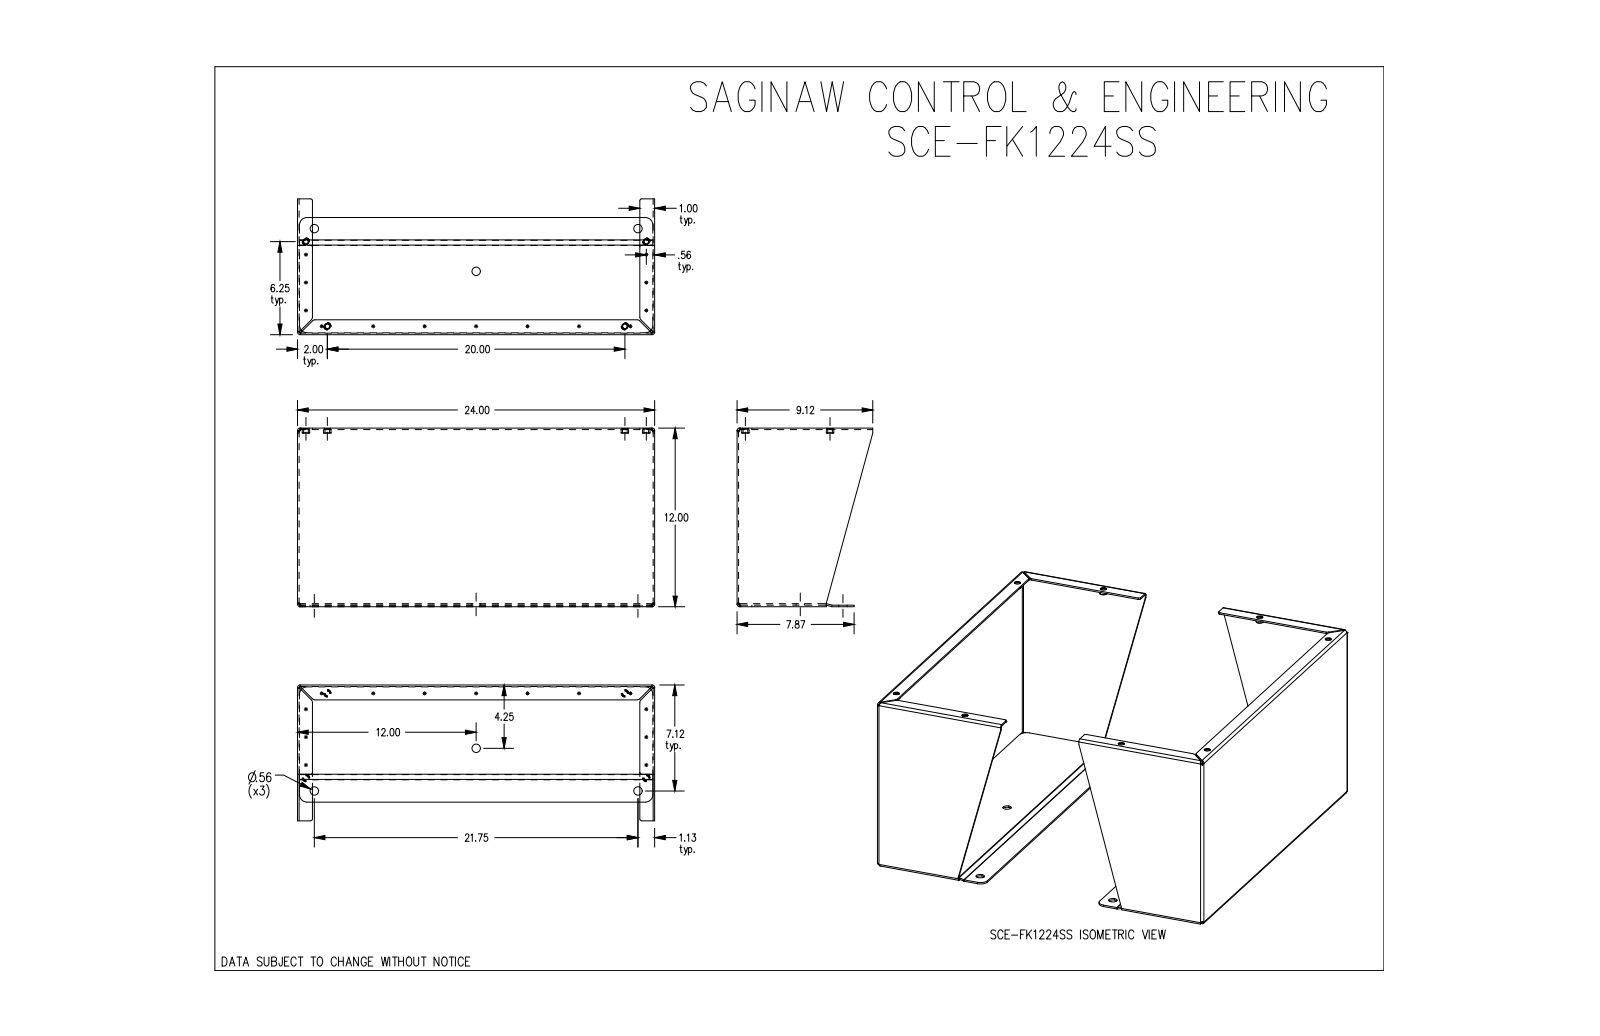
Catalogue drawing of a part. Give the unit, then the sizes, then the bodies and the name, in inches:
Units: inches
Overall size (bounding box): 24 × 24 × 12
Round holes (diameter × count): ⌀0.312 ×8, ⌀0.413 ×8, ⌀0.563 ×6
Round bosses / shafts (diameter × count): ⌀0.5 ×8, ⌀0.412 ×8
Partial cylindrical surfaces — rounded edges, fillets, slot ends (radius × count): R0.166 ×16, R0.063 ×12, R0.125 ×8, R0.22 ×8, R0.5 ×8, R0.062 ×6
Main face-to-face distances: 0.104, 23.896, 23.792, 24, 0.101, 11.893, 11.792, 11.896, 0.205, 11.789
Hole centre spacings: 1.035, 5.866, 6.614, 10.646, 10.659, 11.611, 16.343, 17.247
Volume: 148 in³ · Surface area: 2 887 in²
Bodies: 12 solids, 286 faces (120 planar, 110 cylindrical, 56 other)
Part name (STEP PRODUCT): SCE-FK1224SS
STEP written by: SolidWorks 2019 (CONFIG_CONTROL_DESIGN)
